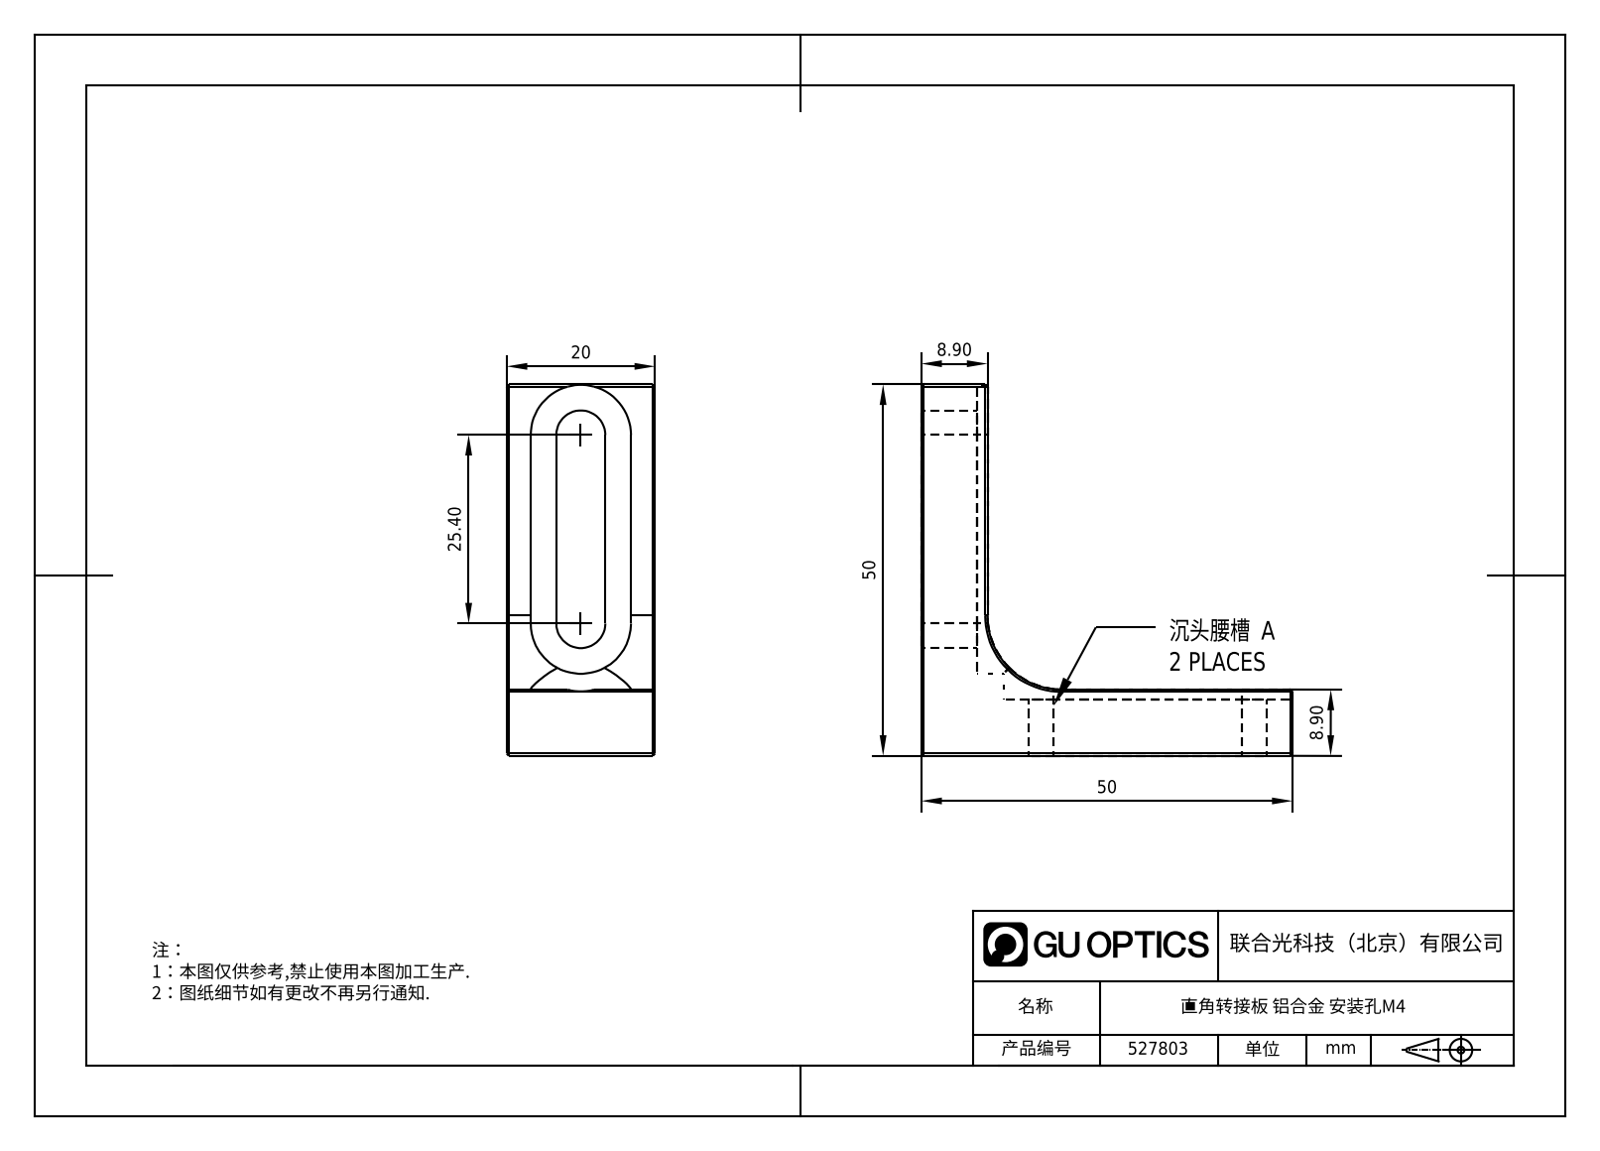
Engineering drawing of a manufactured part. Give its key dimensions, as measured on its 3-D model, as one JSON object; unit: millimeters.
{"part_name": "7.5.4.8_MCS-50A1_面包板垂直支架50mm，带M4双边沉头槽", "step_written_by": "SolidWorks 2021 (CONFIG_CONTROL_DESIGN)", "units": "millimeters", "bodies": {"solids": 1, "faces": 60, "planar": 45, "cylindrical": 13, "other": 2}, "overall_size": [50, 50, 20], "volume_mm3": 13572, "surface_area_mm2": 6205, "partial_cylinders_radius": [[2.3, 4], [5.25, 4], [10, 1]], "face_to_face_distances": [20, 7.7, 12.3, 8.9, 7.5, 1.4, 4.6, 50, 42.5, 41.1]}
